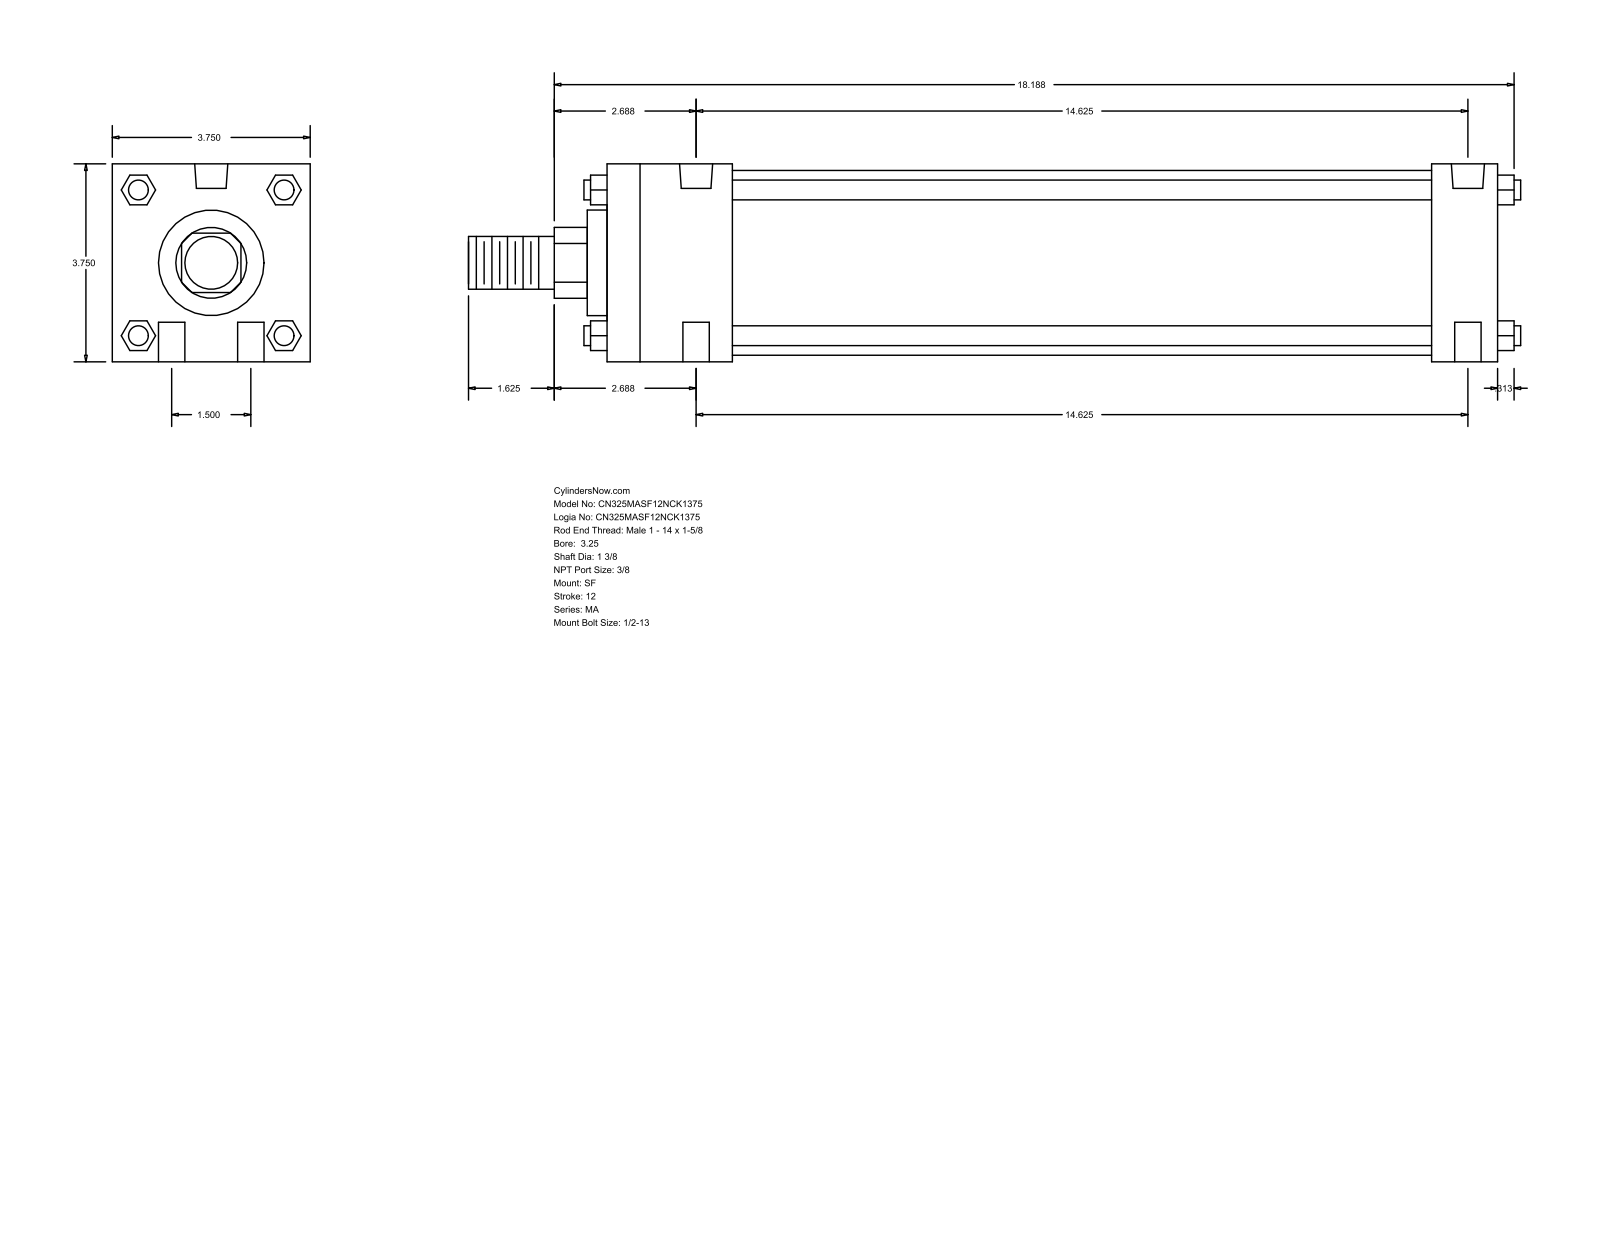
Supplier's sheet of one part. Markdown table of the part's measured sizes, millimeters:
| quantity | value |
| --- | --- |
| part name | MA_SF__0325_1.375 |
| STEP written by | GSSL Pune (CONFIG_CONTROL_DESIGN) |
| units | millimeters |
| bodies | 0 solids, 124 faces (94 planar, 30 cylindrical, 0 other) |
| overall size | 506.41 × 95.25 × 95.25 |
| round holes (diameter × count) | 12.7 × 4, 11.11 × 2, 15.93 × 2 |
| round bosses / shafts (diameter × count) | 9.53 × 4, 88.9 × 1, 50.8 × 1, 34.92 × 1, 25.4 × 1 |
| partial cylindrical surfaces (radius × count) | 17.06 × 1 |
| main face-to-face distances | 95.24, 428.62, 396.87, 31.75, 60.32, 336.55, 368.3, 9.52, 69.84, 406.39 |
| hole center spacings | 19.05, 371.97, 371.48, 38.1, 373.43, 361.95 |
